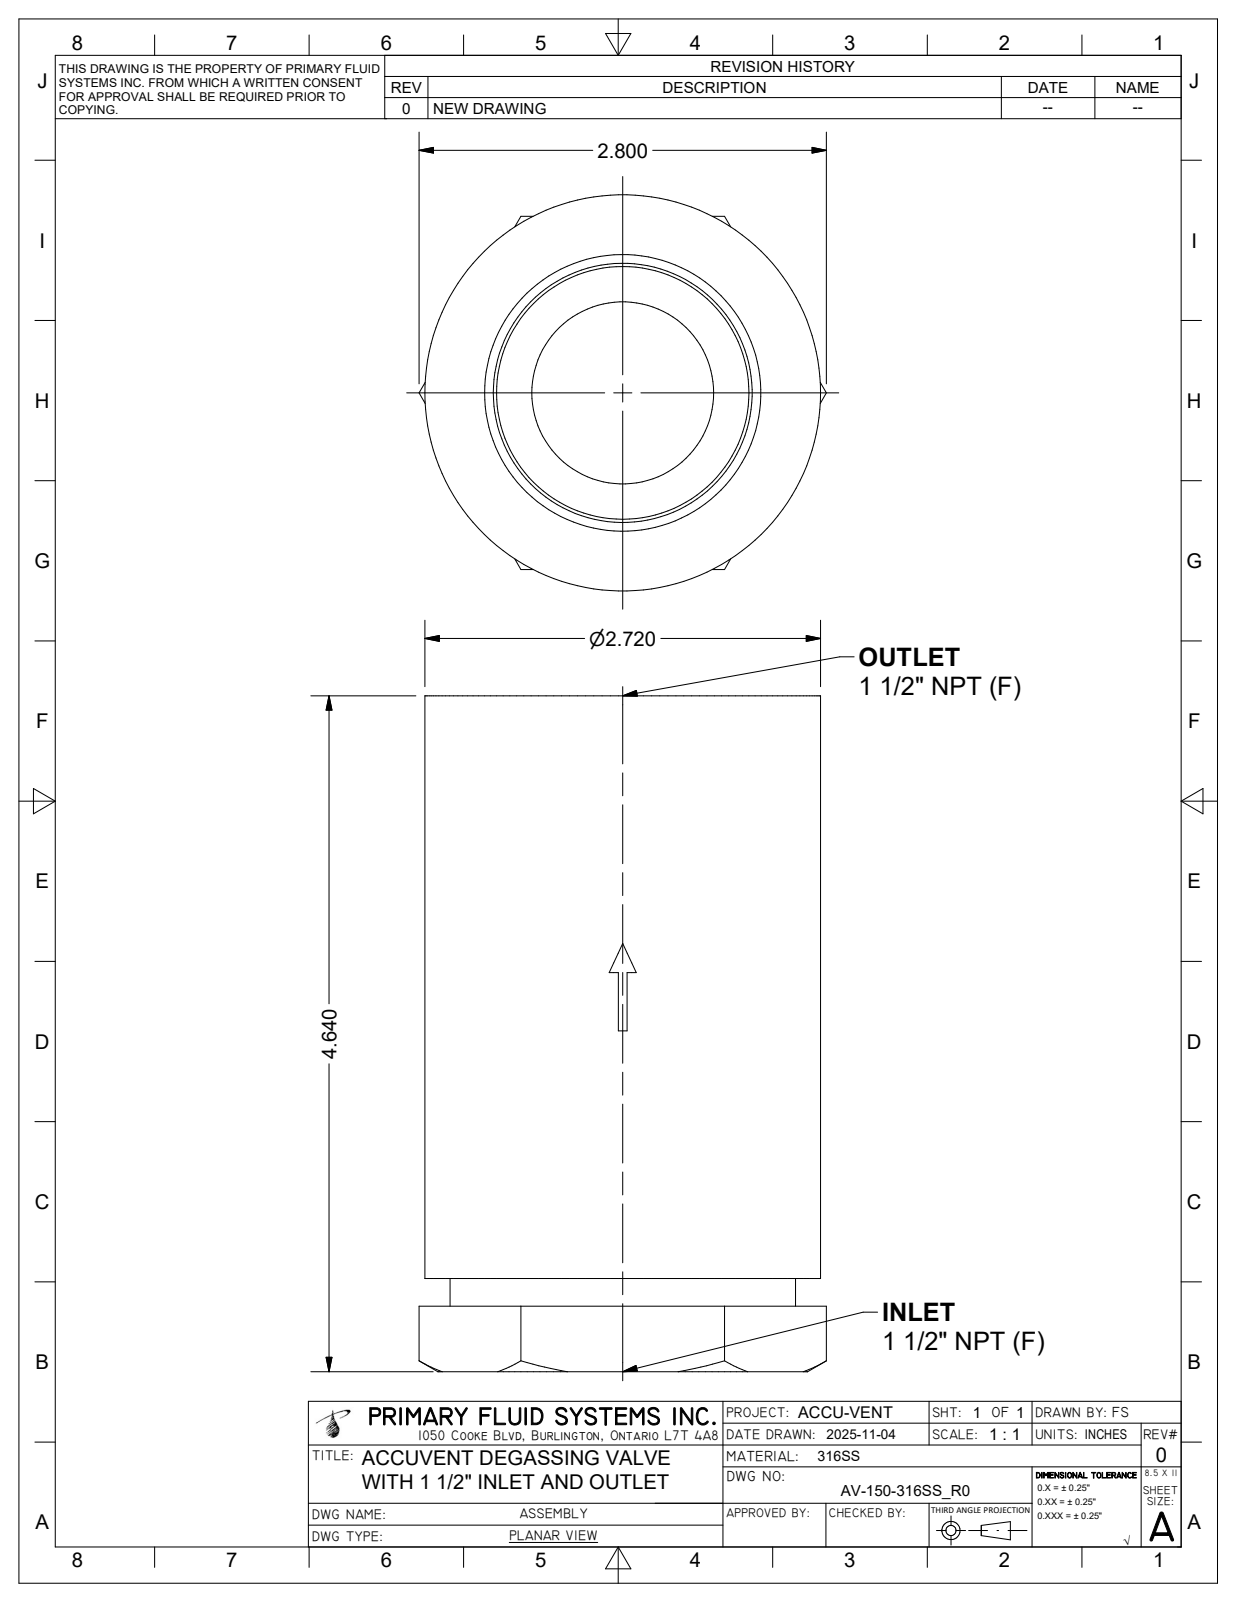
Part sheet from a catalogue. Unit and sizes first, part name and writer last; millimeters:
Units: millimetres
Overall size (bounding box): 117.9 × 71.1 × 69.1
Round holes (diameter × count): ⌀31.8 ×1, ⌀44 ×1, ⌀52.1 ×1, ⌀52.3 ×1, ⌀61.5 ×1
Round bosses / shafts (diameter × count): ⌀69.1 ×1, ⌀60.3 ×1
Partial cylindrical surfaces — rounded edges, fillets, slot ends (radius × count): R34.4 ×1
Main face-to-face distances: 117.9, 61.6, 16.3, 101.6, 98.3, 82, 19.6, 36.8, 20.6, 61.5
Volume: 231 100 mm³ · Surface area: 58 170 mm²
Bodies: 2 solids, 43 faces (22 planar, 8 cylindrical, 13 other)
Part name (STEP PRODUCT): AV-150-316SS_R0; AV-1A-150NPT_R1; BUSHING_200X150_R0
STEP written by: Autodesk Inventor 2026 (AUTOMOTIVE_DESIGN)
